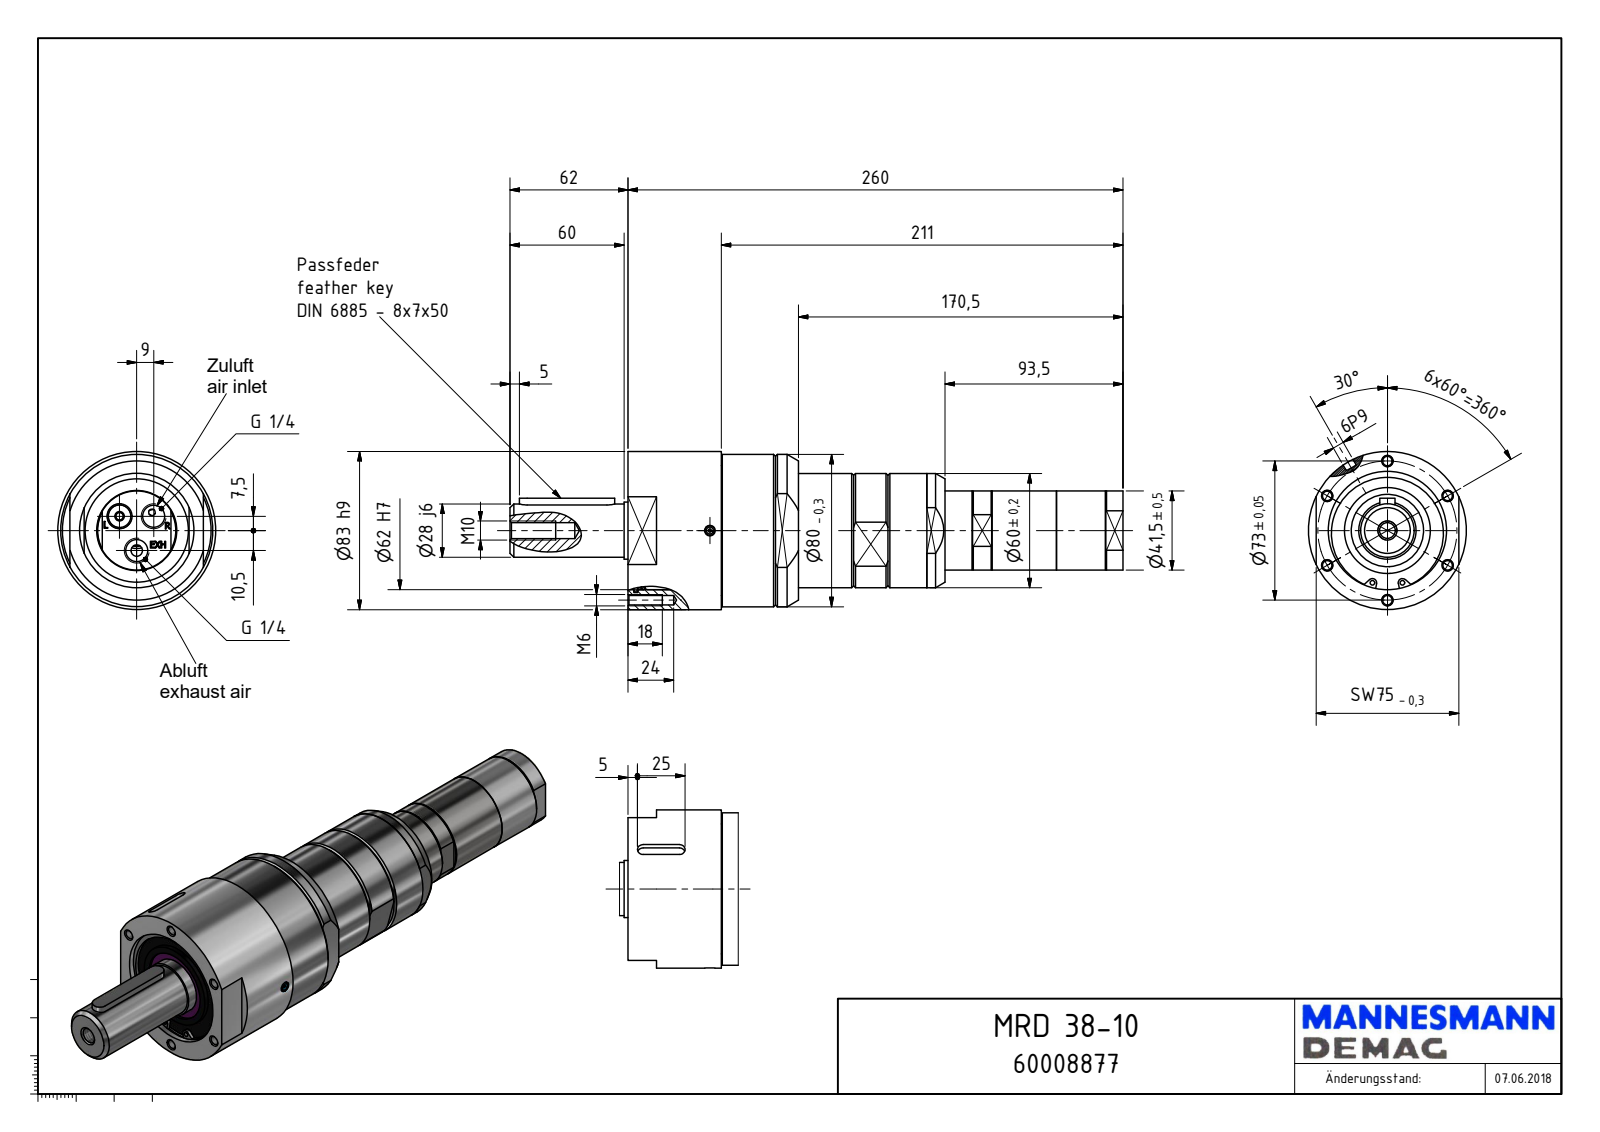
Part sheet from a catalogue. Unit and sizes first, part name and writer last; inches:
Units: inches
Overall size (bounding box): 12.677 × 3.268 × 3.268
Round holes (diameter × count): ⌀0.194 ×6, ⌀0.061 ×3, ⌀0.157 ×3, ⌀0.451 ×3, ⌀0.098 ×2, ⌀0.217 ×2, ⌀0.33 ×1, ⌀1.496 ×1, ⌀1.575 ×1, ⌀1.654 ×1, ⌀2.311 ×1, ⌀2.441 ×1
Round bosses / shafts (diameter × count): ⌀0.197 ×2, ⌀0.142 ×2, ⌀3.268 ×1, ⌀3.15 ×1, ⌀2.684 ×1, ⌀2.638 ×1, ⌀2.362 ×1, ⌀1.772 ×1
Partial cylindrical surfaces — rounded edges, fillets, slot ends (radius × count): R0.138 ×94, R0.089 ×2, R0.118 ×2, R0.157 ×2, R0.974 ×1, R0.983 ×1, R1.28 ×1, R1.306 ×1
Main face-to-face distances: 1.929, 0.02, 3.524, 1.594, 0.098, 1.949, 1.575, 1.831, 0.161, 1.768
Hole centre spacings: 1.437, 2.489, 2.874, 0.461, 0.476, 0.502, 0.732, 0.792
Volume: 50.15 in³ · Surface area: 131.2 in²
Bodies: 1 solid, 568 faces (237 planar, 262 cylindrical, 69 other)
Part name (STEP PRODUCT): MRD 38-10_60008877
STEP written by: Autodesk Inventor 2018 (AUTOMOTIVE_DESIGN)
